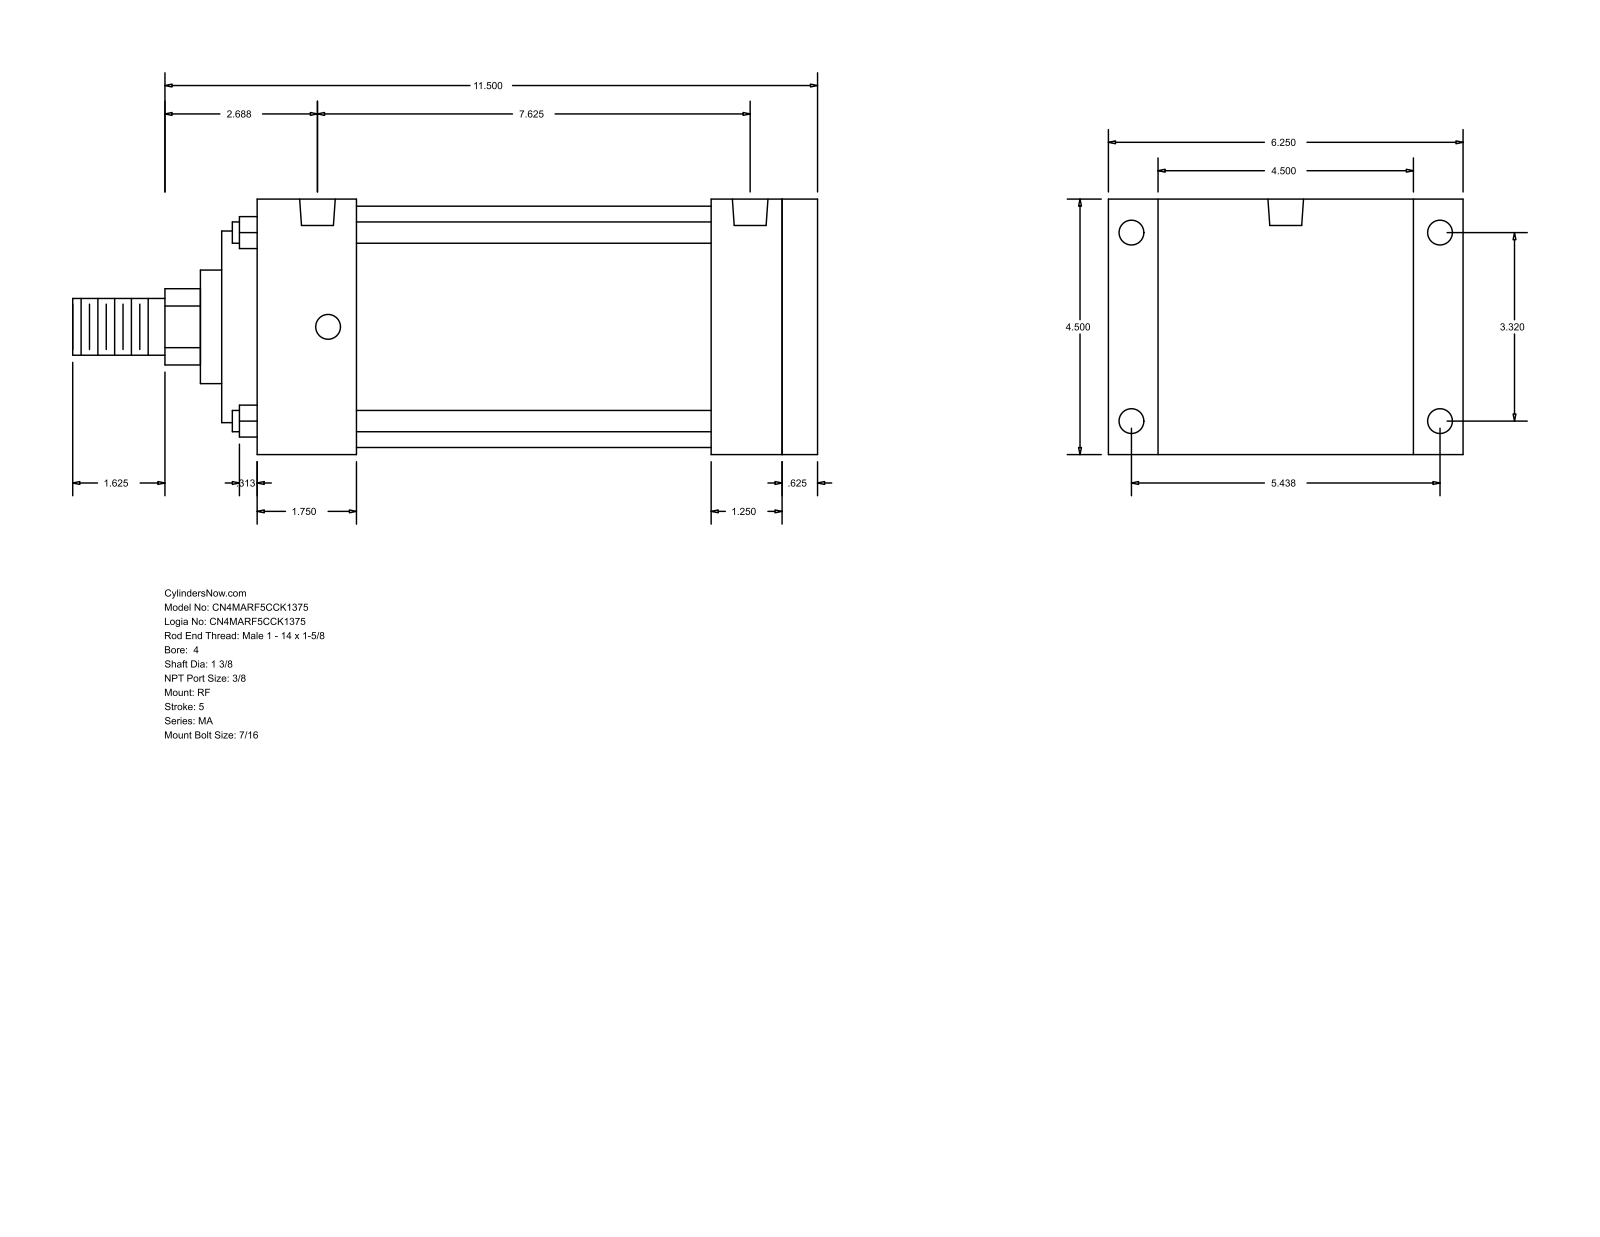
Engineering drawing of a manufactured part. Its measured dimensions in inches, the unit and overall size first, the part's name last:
Units: inches
Overall size (bounding box): 13.125 × 6.25 × 4.5
Round holes (diameter × count): ⌀0.437 ×8, ⌀0.627 ×2
Round bosses / shafts (diameter × count): ⌀0.375 ×4, ⌀4.25 ×1, ⌀3.375 ×1, ⌀2 ×1, ⌀1.375 ×1, ⌀1 ×1
Partial cylindrical surfaces — rounded edges, fillets, slot ends (radius × count): R0.672 ×1
Main face-to-face distances: 4.5, 9.875, 0.625, 9.25, 10.5, 0.875, 5.375, 8.625, 8, 1.25
Hole centre spacings: 3.32, 5.438, 6.371, 7.25, 0.187, 0.188, 7.437, 7.438
Bodies: 0 solids, 94 faces (65 planar, 29 cylindrical, 0 other)
Part name (STEP PRODUCT): MA_RF__0400_1.375
STEP written by: GSSL Pune (CONFIG_CONTROL_DESIGN)
